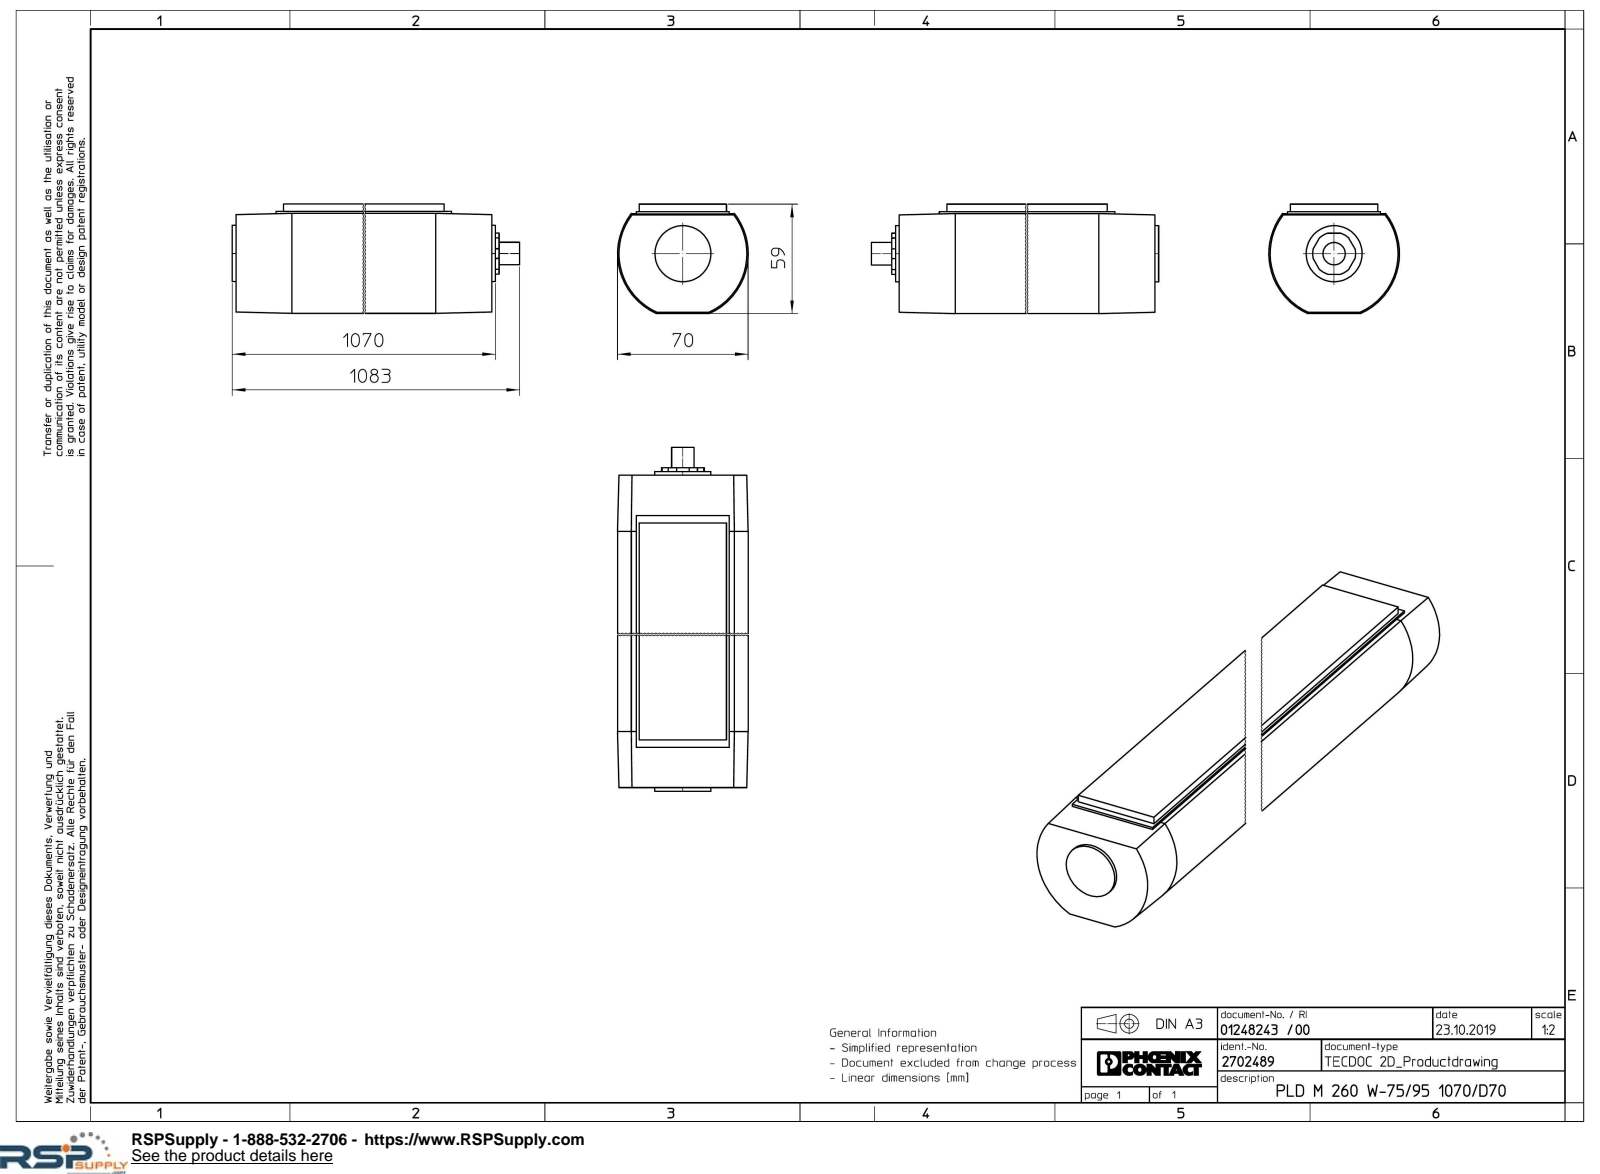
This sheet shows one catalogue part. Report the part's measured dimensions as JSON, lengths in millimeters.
{"part_name": "PLD_M_260_W_75_95_1070_D70-select", "step_written_by": "Creo Elements/Direct Modeling 20.1A 29-Sep-2018 (C) Parametric Technology GmbH (AUTOMOTIVE_DESIGN)", "units": "millimeters", "bodies": {"solids": 1, "faces": 47, "planar": 29, "cylindrical": 14, "other": 4}, "overall_size": [1082.95, 70, 58.5], "volume_mm3": 3728000, "surface_area_mm2": 242256, "round_bosses_or_shafts": [[30, 1], [12, 1]], "partial_cylinders_radius": [[11.5, 1], [35, 1]], "face_to_face_distances": [58.5, 53.5, 5, 46.8, 4, 54.5, 1, 1066, 1.5, 48.3]}
